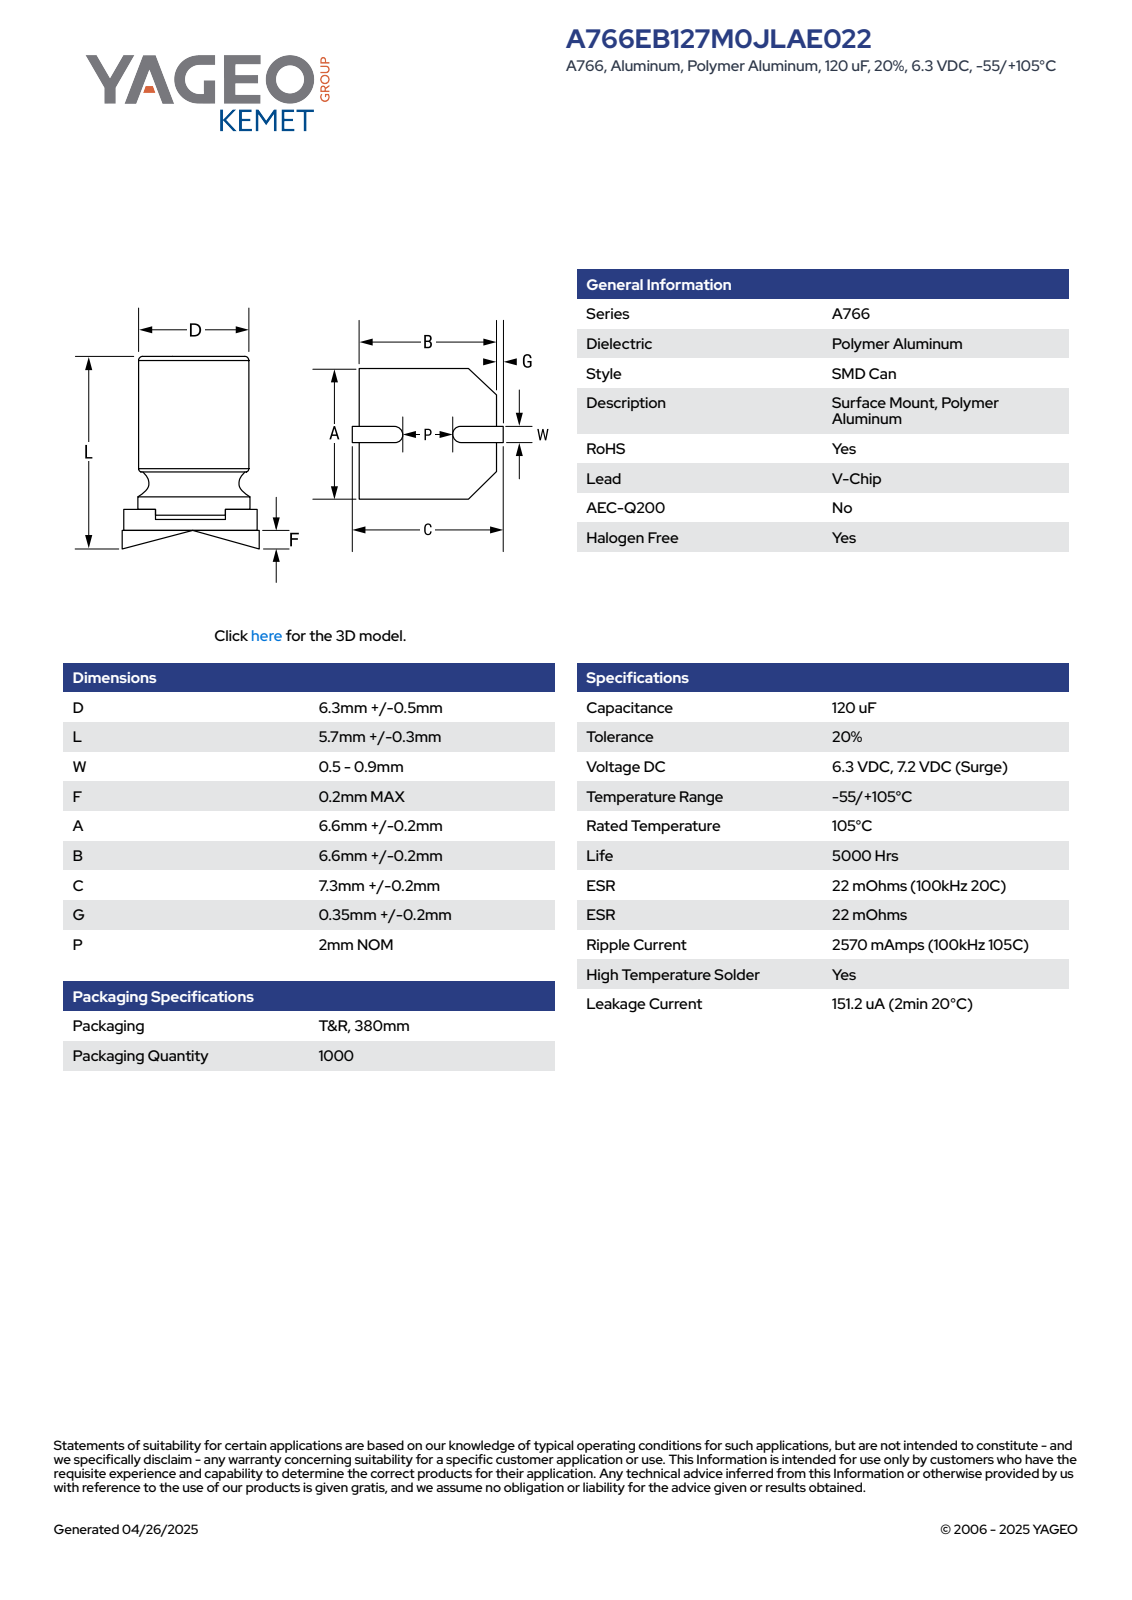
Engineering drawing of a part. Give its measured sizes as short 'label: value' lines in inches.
name: CAC_KS_6.3X5.7_D6.8L6W0.9F0.2A6.8B6.8C7.5P2
written by: SolidWorks 2014 (AUTOMOTIVE_DESIGN)
unit: in
bodies: 5 solids, 76 faces (59 planar, 11 cylindrical, 6 other)
size: 0.295 × 0.268 × 0.236
volume: 0.012 in³; area: 0.479 in²
bosses: 1× ⌀0.256
rounds: 2× R0.008, 1× R0.106, 1× R0.134
face distances: 0.228, 0.217, 0.02, 0.047, 0.268, 0.236, 0.189, 0.169, 0.059, 0.067
